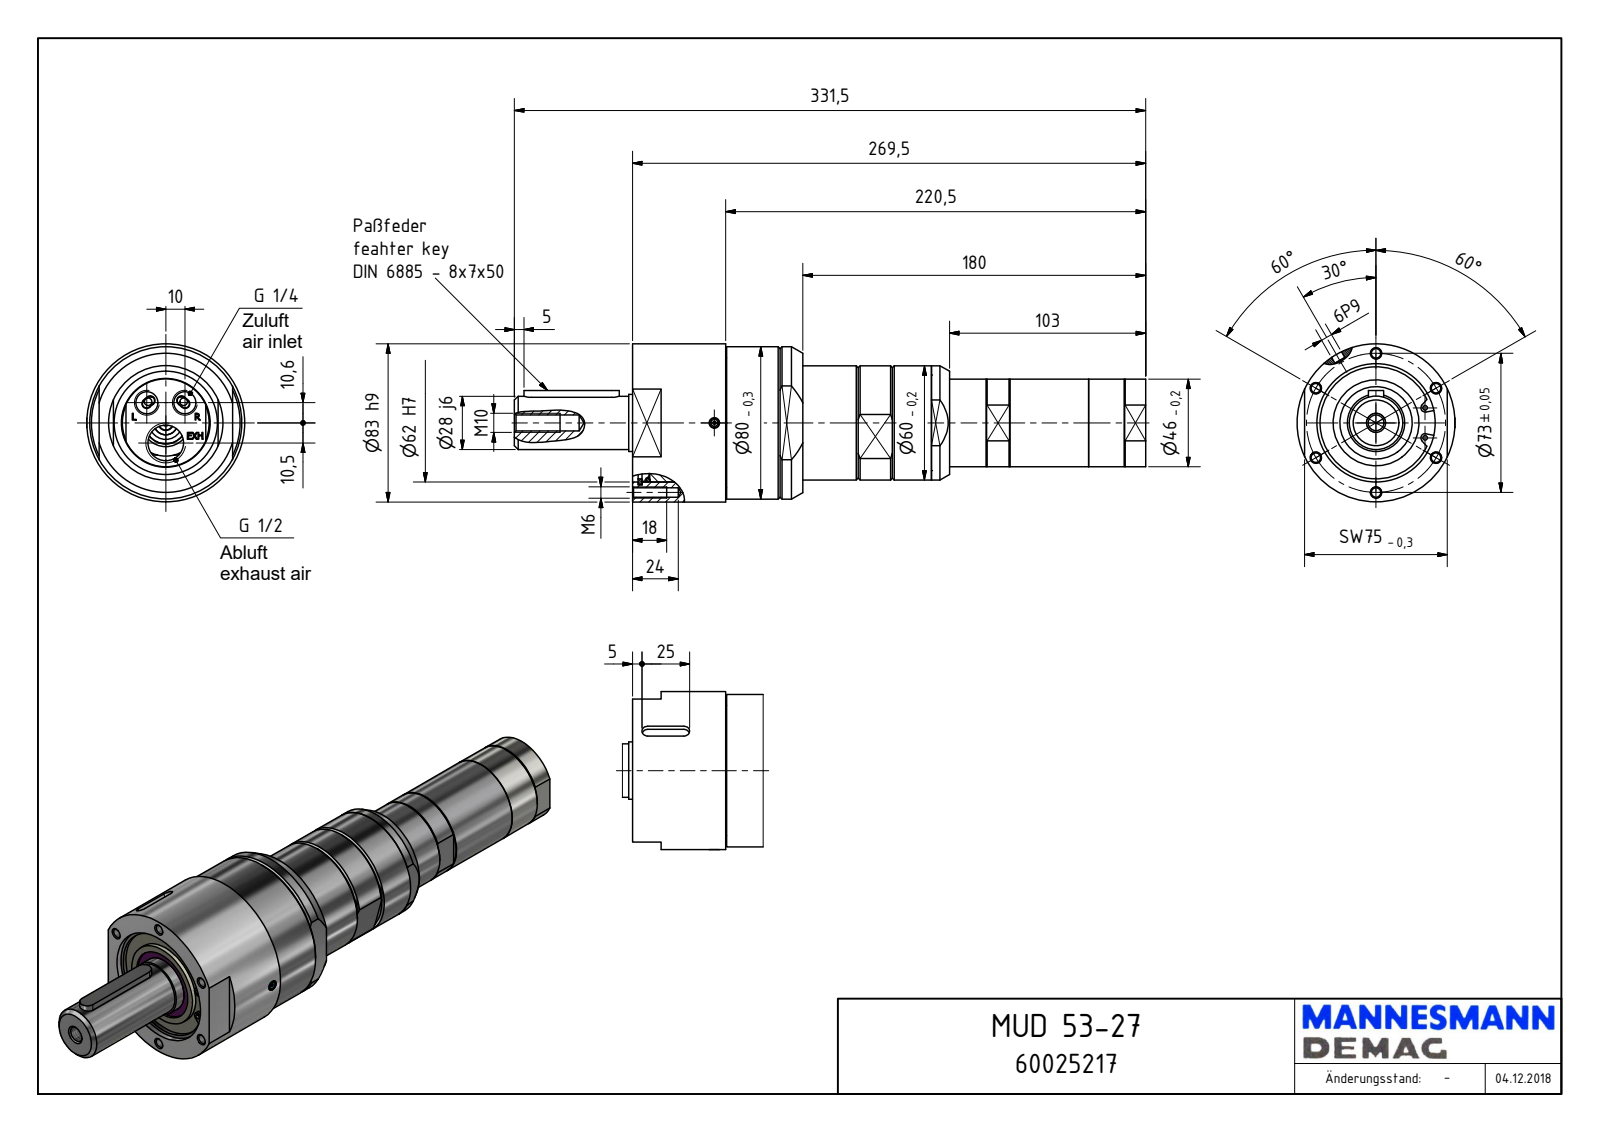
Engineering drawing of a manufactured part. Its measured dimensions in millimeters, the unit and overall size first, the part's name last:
Units: millimetres
Overall size (bounding box): 331.5 × 83 × 83
Round holes (diameter × count): ⌀4.92 ×6, ⌀1.55 ×3, ⌀2.5 ×2, ⌀4 ×2, ⌀5.5 ×2, ⌀11.45 ×2, ⌀8.38 ×1, ⌀18.63 ×1, ⌀36.5 ×1, ⌀38 ×1, ⌀40 ×1, ⌀46.5 ×1
Round bosses / shafts (diameter × count): ⌀5 ×2, ⌀3.6 ×2, ⌀3.3 ×2, ⌀83 ×1, ⌀80 ×1, ⌀68.18 ×1, ⌀67 ×1, ⌀60 ×1
Partial cylindrical surfaces — rounded edges, fillets, slot ends (radius × count): R3.5 ×94, R6.47 ×7, R7.69 ×3, R2.25 ×2, R3 ×2, R4 ×2, R5 ×2, R17.43 ×1
Main face-to-face distances: 49, 2.5, 0.5, 5, 157, 108, 67.5, 89.5, 40.5, 44
Hole centre spacings: 36.5, 63.22, 73, 11.89, 14.57, 22.92, 23.35, 26.77
Volume: 863 325 mm³ · Surface area: 89 782 mm²
Bodies: 1 solid, 606 faces (233 planar, 290 cylindrical, 83 other)
Part name (STEP PRODUCT): MUD 53-27_60025217
STEP written by: Autodesk Inventor 2018 (AUTOMOTIVE_DESIGN)
